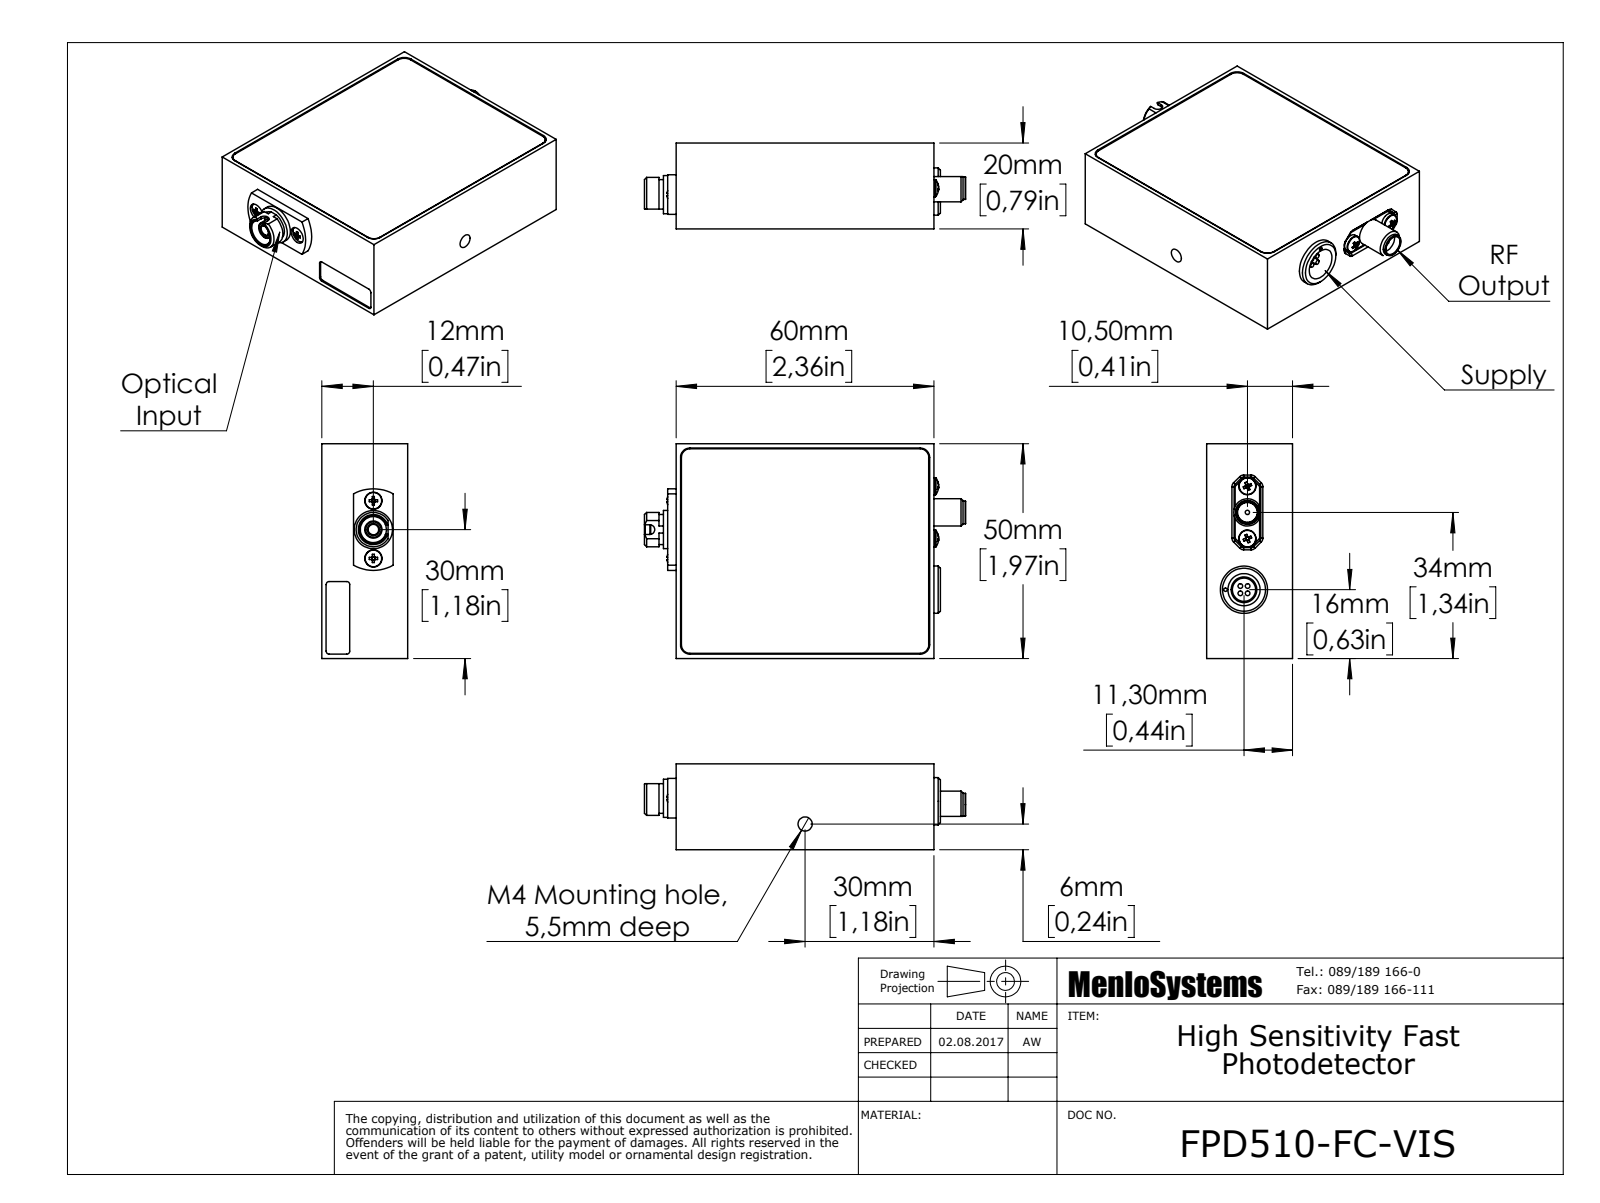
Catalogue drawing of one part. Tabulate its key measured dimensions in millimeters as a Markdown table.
| quantity | value |
| --- | --- |
| part name | FPD510-FC-VIS_170721 |
| STEP written by | SolidWorks 2016 (AUTOMOTIVE_DESIGN) |
| units | millimeters |
| bodies | 21 solids, 1105 faces (470 planar, 296 cylindrical, 339 other) |
| overall size | 74.8 × 50 × 20 |
| volume | 38 946 mm³ |
| surface area | 28 672 mm² |
| round holes (diameter × count) | 1.6 × 23, 2.2 × 12, 4 × 12, 2.6 × 2, 0.8 × 1, 1 × 1, 2.43 × 1, 3.2 × 1, 3.3 × 1, 4.6 × 1, 6.07 × 1, 7.5 × 1 |
| round bosses / shafts (diameter × count) | 2 × 14, 3.8 × 10, 4 × 4, 1.1 × 4, 0.45 × 3, 11 × 1, 9 × 1, 8.95 × 1 |
| partial cylindrical surfaces (radius × count) | 2.2 × 26, 0.7 × 8, 0.8 × 8, 2 × 8, 1.4 × 4, 1.5 × 2, 1.12 × 1, 8 × 1 |
| main face-to-face distances | 1.5, 0.35, 19.55, 18.05, 1.85, 19.9, 6.5, 7, 50, 12.9 |
| hole center spacings | 4.21, 9.27, 10.5, 14.96, 16.5, 19.36, 20, 21.82 |
